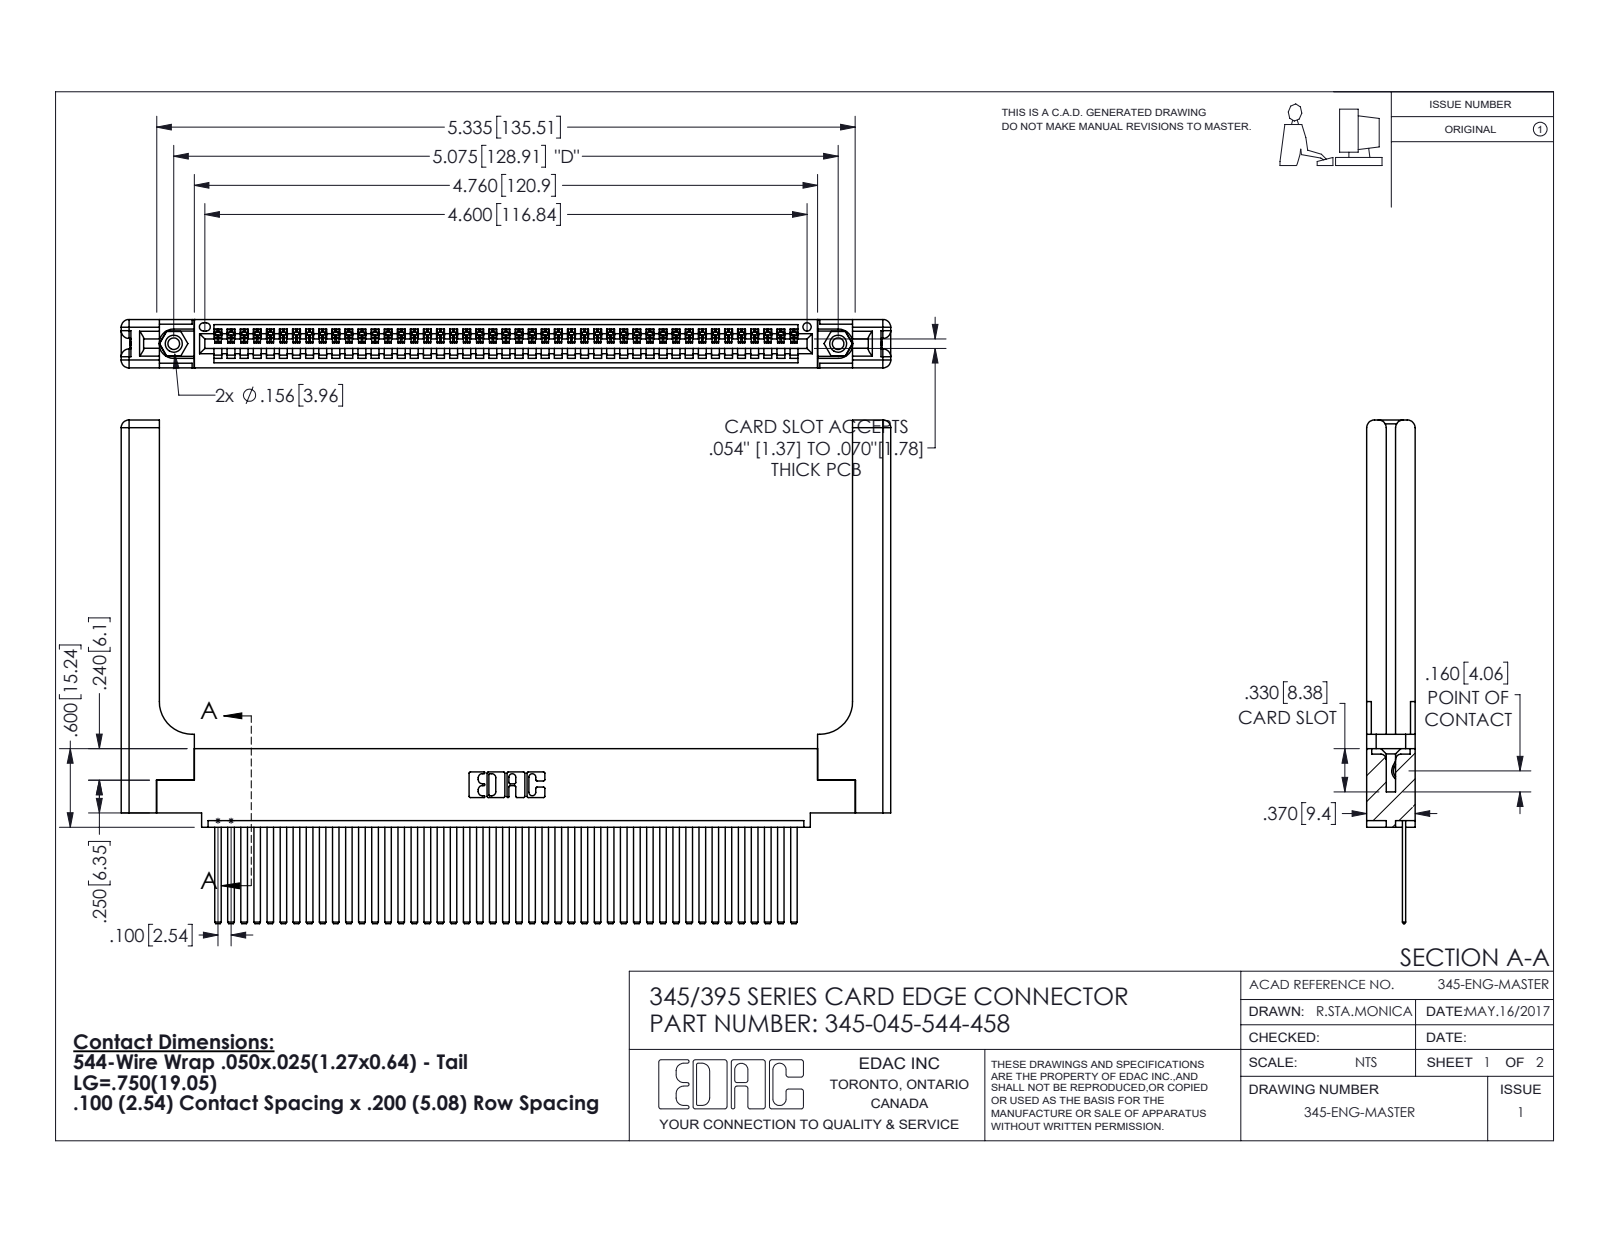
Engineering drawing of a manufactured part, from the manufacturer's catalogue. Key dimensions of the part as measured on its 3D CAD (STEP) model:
Part name (STEP PRODUCT): 345 Part_0.110 Offset - 0.156 Dia-TH; 345-292-001_345-293-144; 345-250-001_345-250-001-102; 345-220-058_345-220-058 (+1 more)
STEP written by: SolidWorks 2016 (CONFIG_CONTROL_DESIGN)
Units: inches
Bodies: 50 solids, 2726 faces (1852 planar, 814 cylindrical, 60 other)
Overall size (bounding box): 5.879 × 3.847 × 0.37
Volume: 1.413 in³ · Surface area: 41.03 in²
Round holes (diameter × count): ⌀0.089 ×2, ⌀0.125 ×2, ⌀0.156 ×2, ⌀0.064 ×1
Round bosses / shafts (diameter × count): ⌀0.155 ×2
Partial cylindrical surfaces — rounded edges, fillets, slot ends (radius × count): R0.006 ×90, R0.01 ×22, R0.06 ×16, R0.007 ×6, R0.031 ×6, R0.026 ×3, R0.03 ×2, R0.031 ×2
Main face-to-face distances: 0.072, 0.298, 0.37, 0.098, 0.272, 0.025, 0.2, 0.225, 0.148, 0.15
Hole centre spacings: 0.27, 4.839, 5.075
